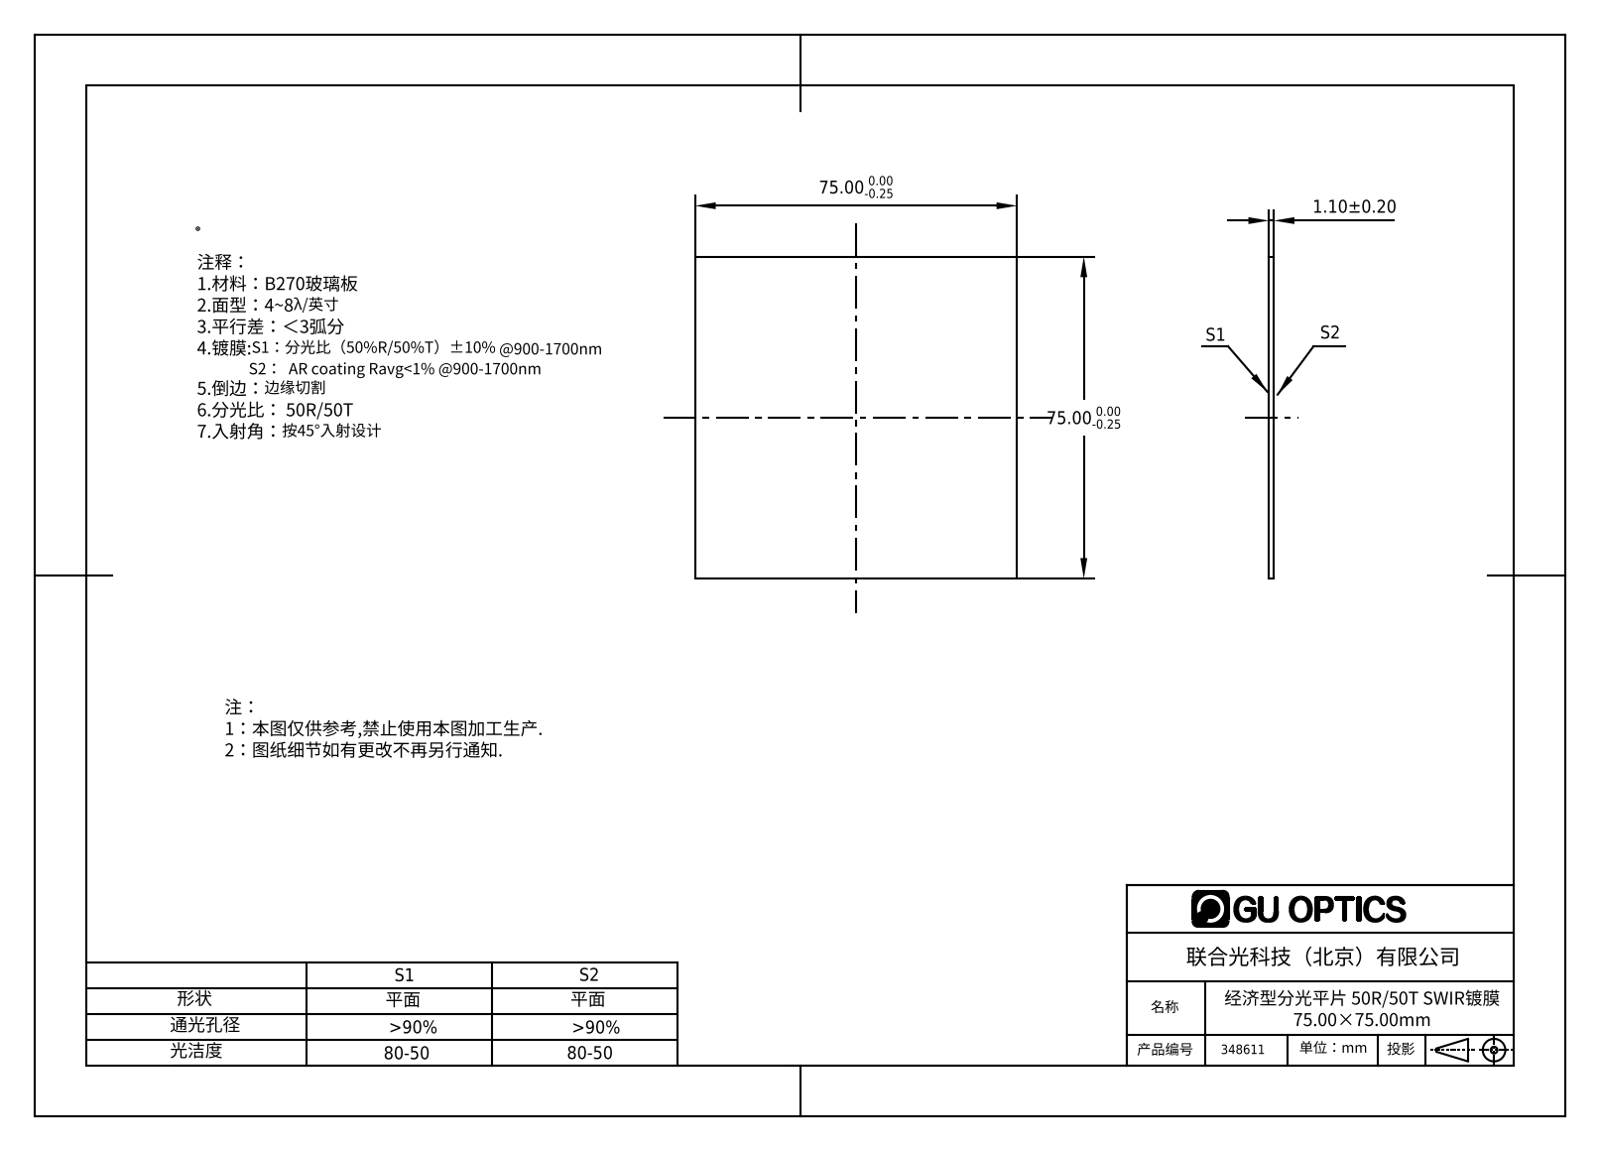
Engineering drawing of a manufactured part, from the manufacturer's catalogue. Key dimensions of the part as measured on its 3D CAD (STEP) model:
Part name (STEP PRODUCT): 348513
STEP written by: SolidWorks 2016 (CONFIG_CONTROL_DESIGN)
Units: millimetres
Bodies: 1 solid, 6 faces (6 planar, 0 cylindrical, 0 other)
Overall size (bounding box): 75 × 75 × 1.1
Volume: 6 188 mm³ · Surface area: 11 580 mm²
Main face-to-face distances: 1.1, 75
